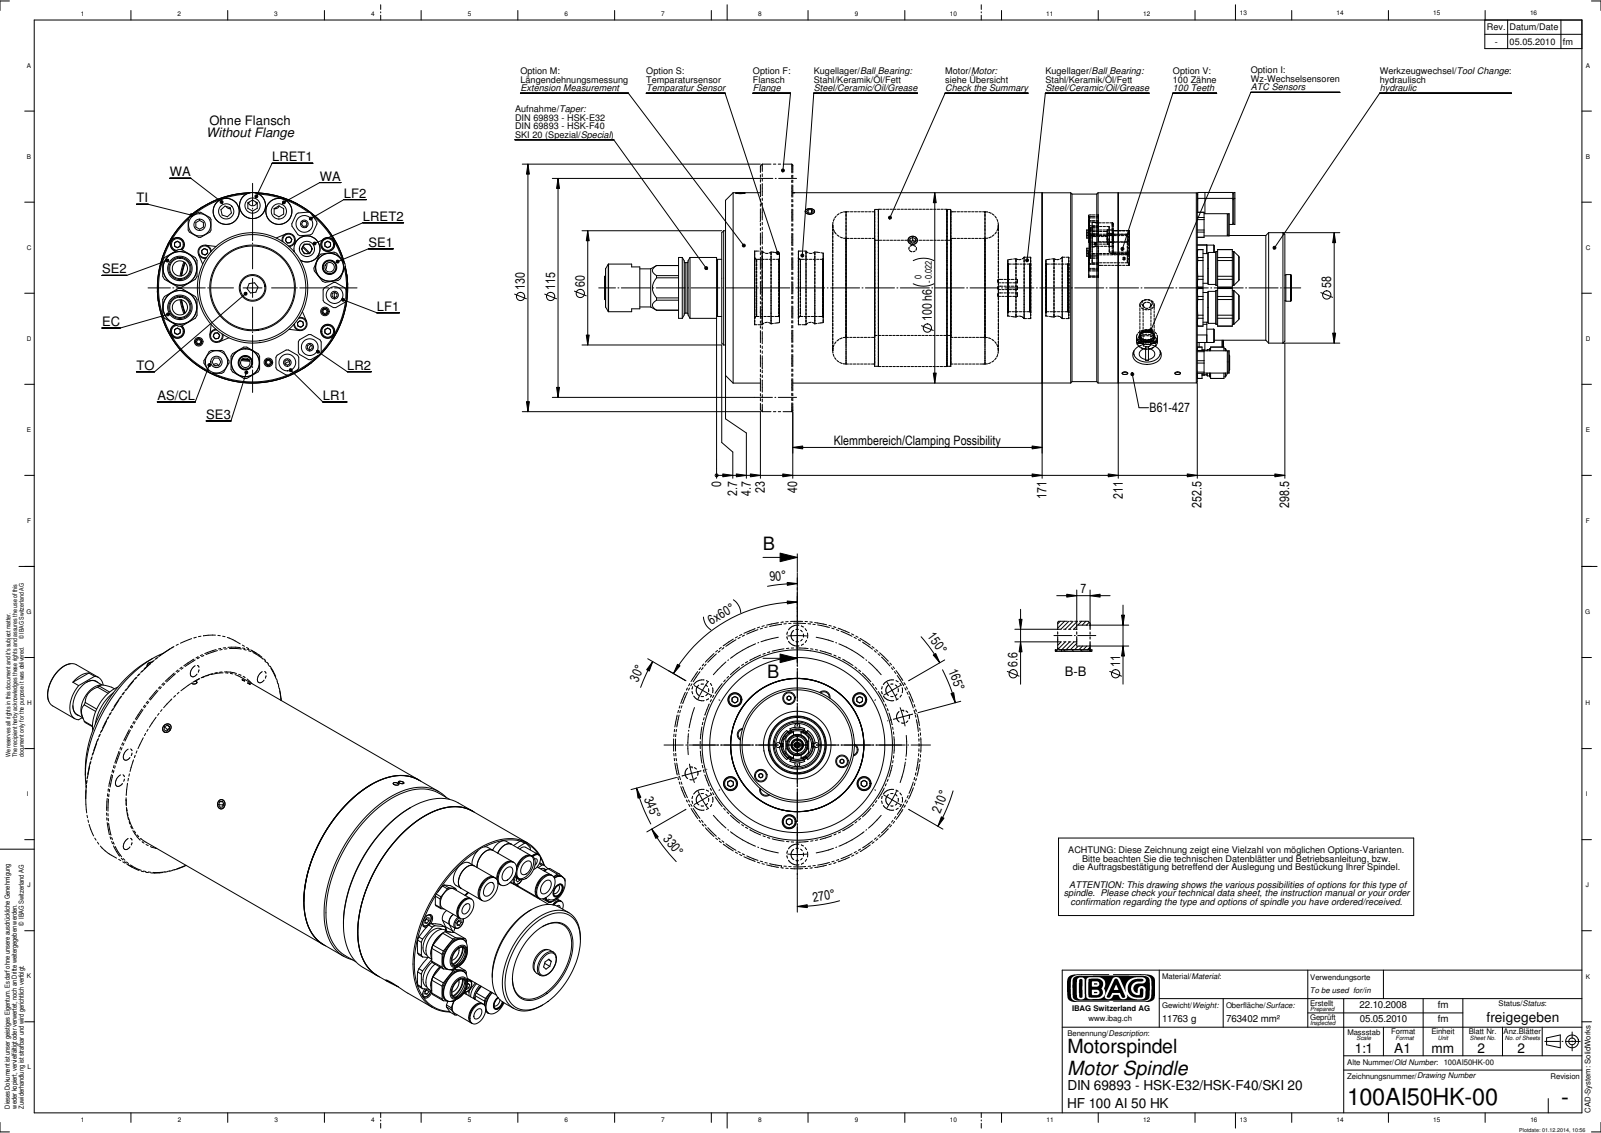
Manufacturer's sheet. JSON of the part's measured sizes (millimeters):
{"part_name": "100AI50HK-00", "step_written_by": "SolidWorks 2012 (CONFIG_CONTROL_DESIGN)", "units": "millimeters", "bodies": {"solids": 0, "faces": 865, "planar": 353, "cylindrical": 325, "other": 187}, "overall_size": [360.86, 100.1, 100.05], "round_holes": [[7.4, 9], [8, 6], [4, 4], [4.5, 3], [5, 3], [15, 3], [6, 2], [6.7, 2], [10.7, 2], [16.2, 2], [10, 1], [35.5, 1]], "round_bosses_or_shafts": [[5.7, 6], [13.7, 4], [13.7, 4], [8.8, 4], [7, 4], [17.8, 2], [16.79, 2], [15.59, 2]], "partial_cylinders_radius": [[5, 6], [6.6, 6], [8.25, 2], [9.9, 2], [11.75, 1]], "face_to_face_distances": [206.3, 247.8, 41.5, 18.3, 188, 229.5, 2, 20.3, 208.3, 249.8], "hole_center_spacings": [43.25, 45.6, 39.5, 40, 40.5, 72.27, 72.54, 5.1]}
